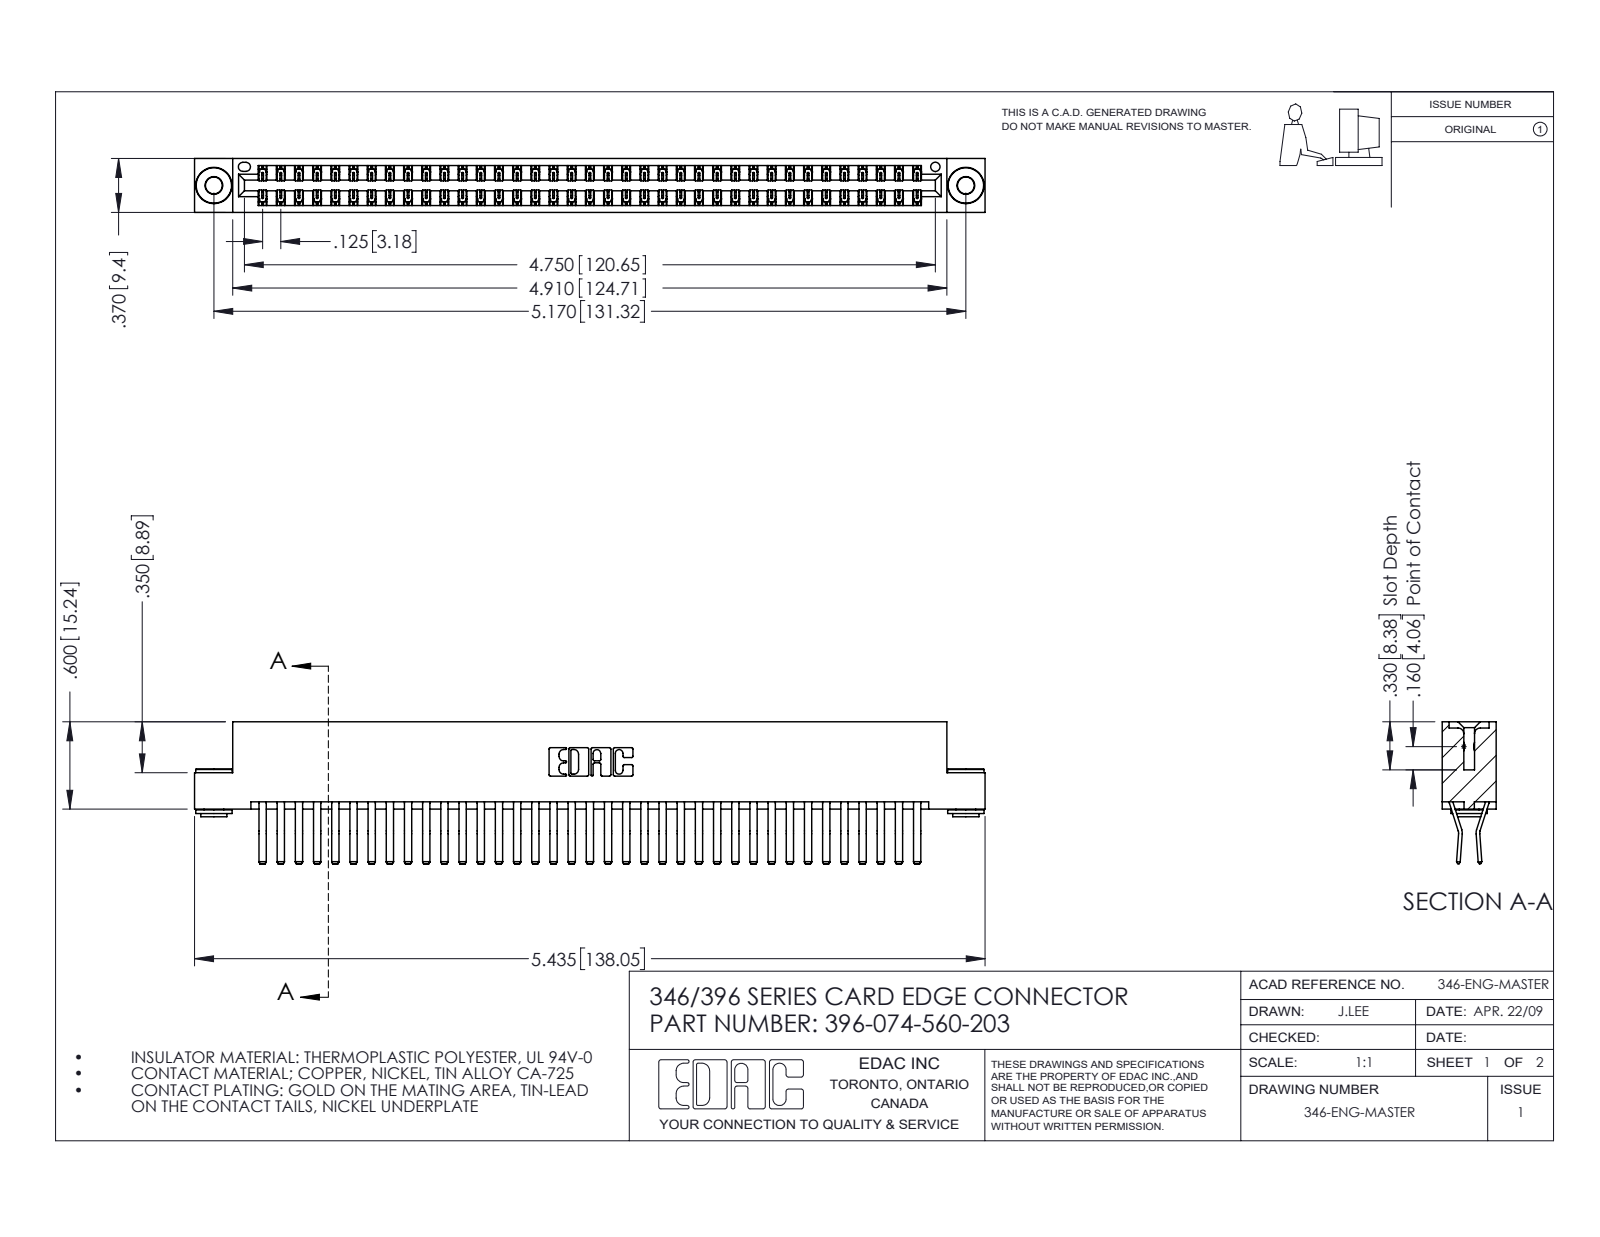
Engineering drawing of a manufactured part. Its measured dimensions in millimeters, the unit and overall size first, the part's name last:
Units: millimetres
Overall size (bounding box): 138 × 24.8 × 9.4
Round holes (diameter × count): ⌀2.9 ×2, ⌀4 ×2, ⌀1.6 ×1
Round bosses / shafts (diameter × count): ⌀6.4 ×2, ⌀4.6 ×2, ⌀3.5 ×2
Partial cylindrical surfaces — rounded edges, fillets, slot ends (radius × count): R0.2 ×111, R0.3 ×22, R0.2 ×6, R0.8 ×6, R0.7 ×3, R0.3 ×2, R0.4 ×2, R0.6 ×2
Main face-to-face distances: 1.2, 8.2, 9.4, 6.4, 0.6, 1.8, 7.6, 7, 3.8, 5.6
Hole centre spacings: 6.2, 126, 131.3
Volume: 13 900 mm³ · Surface area: 20 570 mm²
Bodies: 77 solids, 4156 faces (2676 planar, 1472 cylindrical, 8 other)
Part name (STEP PRODUCT): 345-292-001_560 Tail; 396-074-560-203; 346 Part_Flush Mounting Lugs - 0.156 Dia-TH; 345-250-002_345-250-002-102
STEP written by: SolidWorks 2016 (CONFIG_CONTROL_DESIGN)
